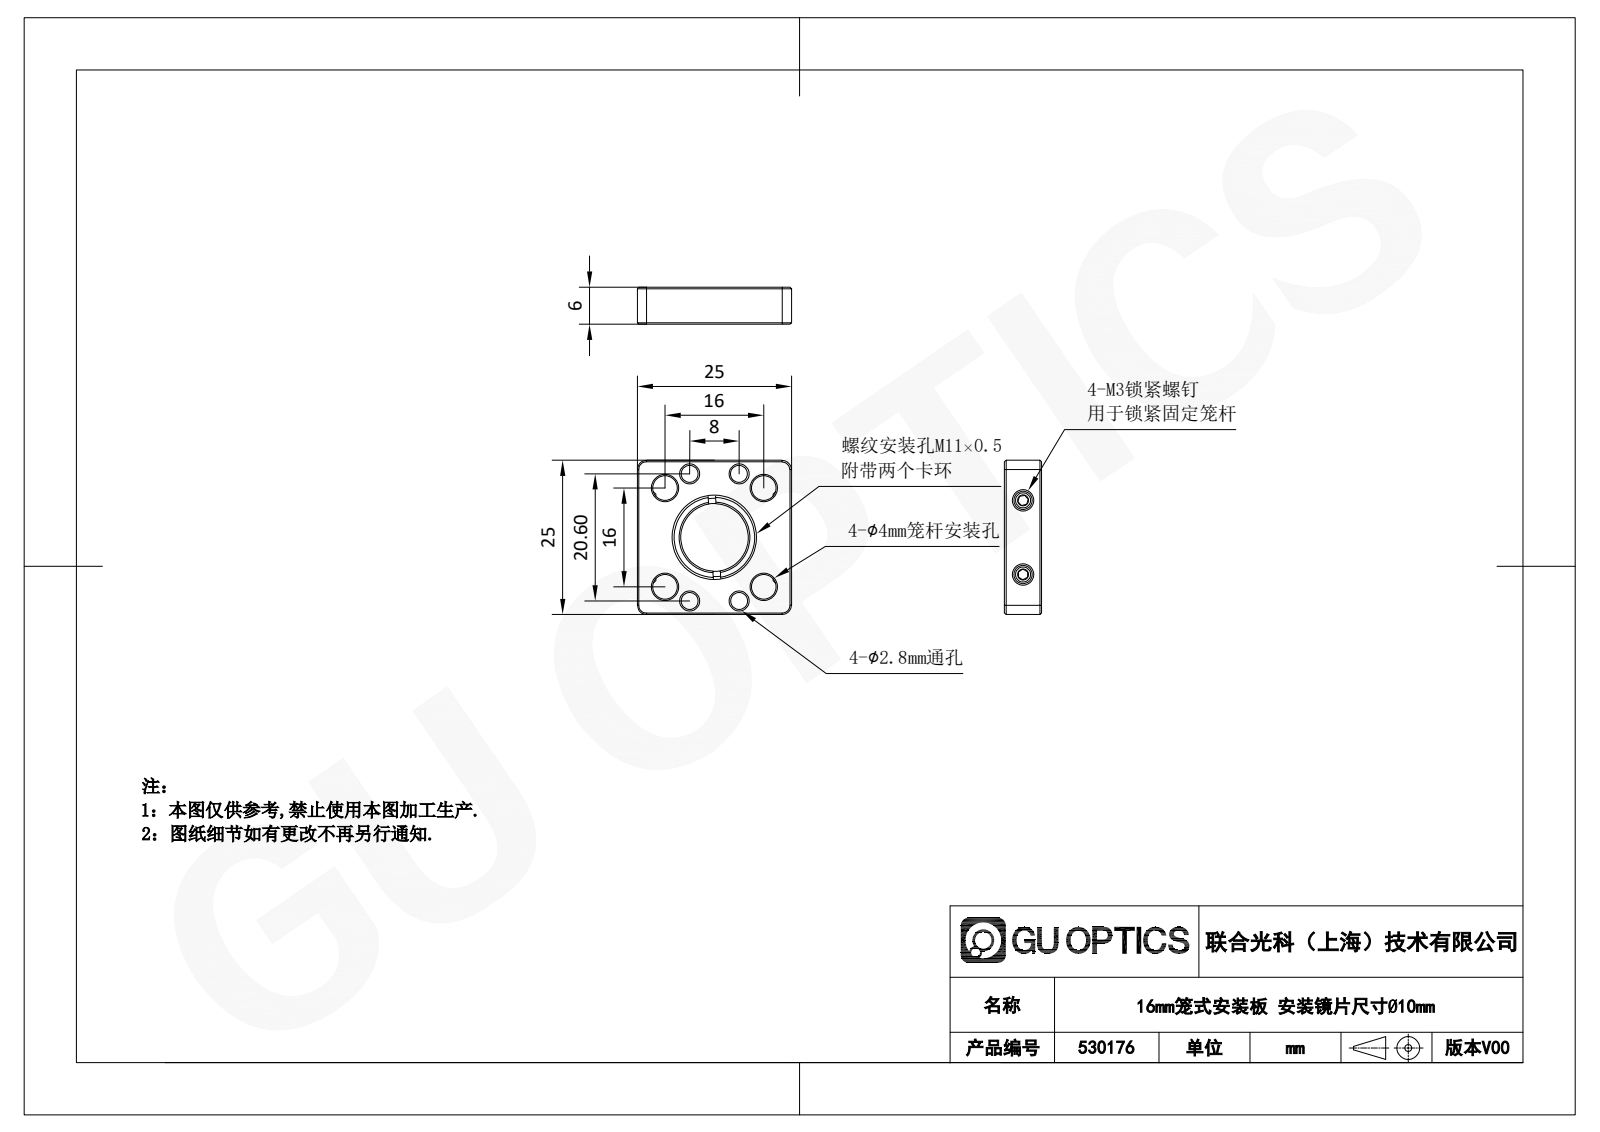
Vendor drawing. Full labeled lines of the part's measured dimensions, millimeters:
Part name (STEP PRODUCT): 530176
STEP written by: SolidWorks 2020 (CONFIG_CONTROL_DESIGN)
Units: millimetres
Bodies: 7 solids, 287 faces (136 planar, 25 cylindrical, 126 other)
Overall size (bounding box): 25 × 25 × 6
Volume: 2 898 mm³ · Surface area: 2 787 mm²
Round holes (diameter × count): ⌀2.8 ×4, ⌀4 ×4, ⌀2.5 ×2, ⌀8 ×1, ⌀10.5 ×1
Round bosses / shafts (diameter × count): ⌀3 ×2, ⌀11 ×1
Partial cylindrical surfaces — rounded edges, fillets, slot ends (radius × count): R1.5 ×4
Main face-to-face distances: 6, 25, 2, 4, 21.56, 3, 22, 1.5, 1, 24
Hole centre spacings: 4.61, 11.05, 11.31, 12.22, 16, 18.73, 21.88, 8
